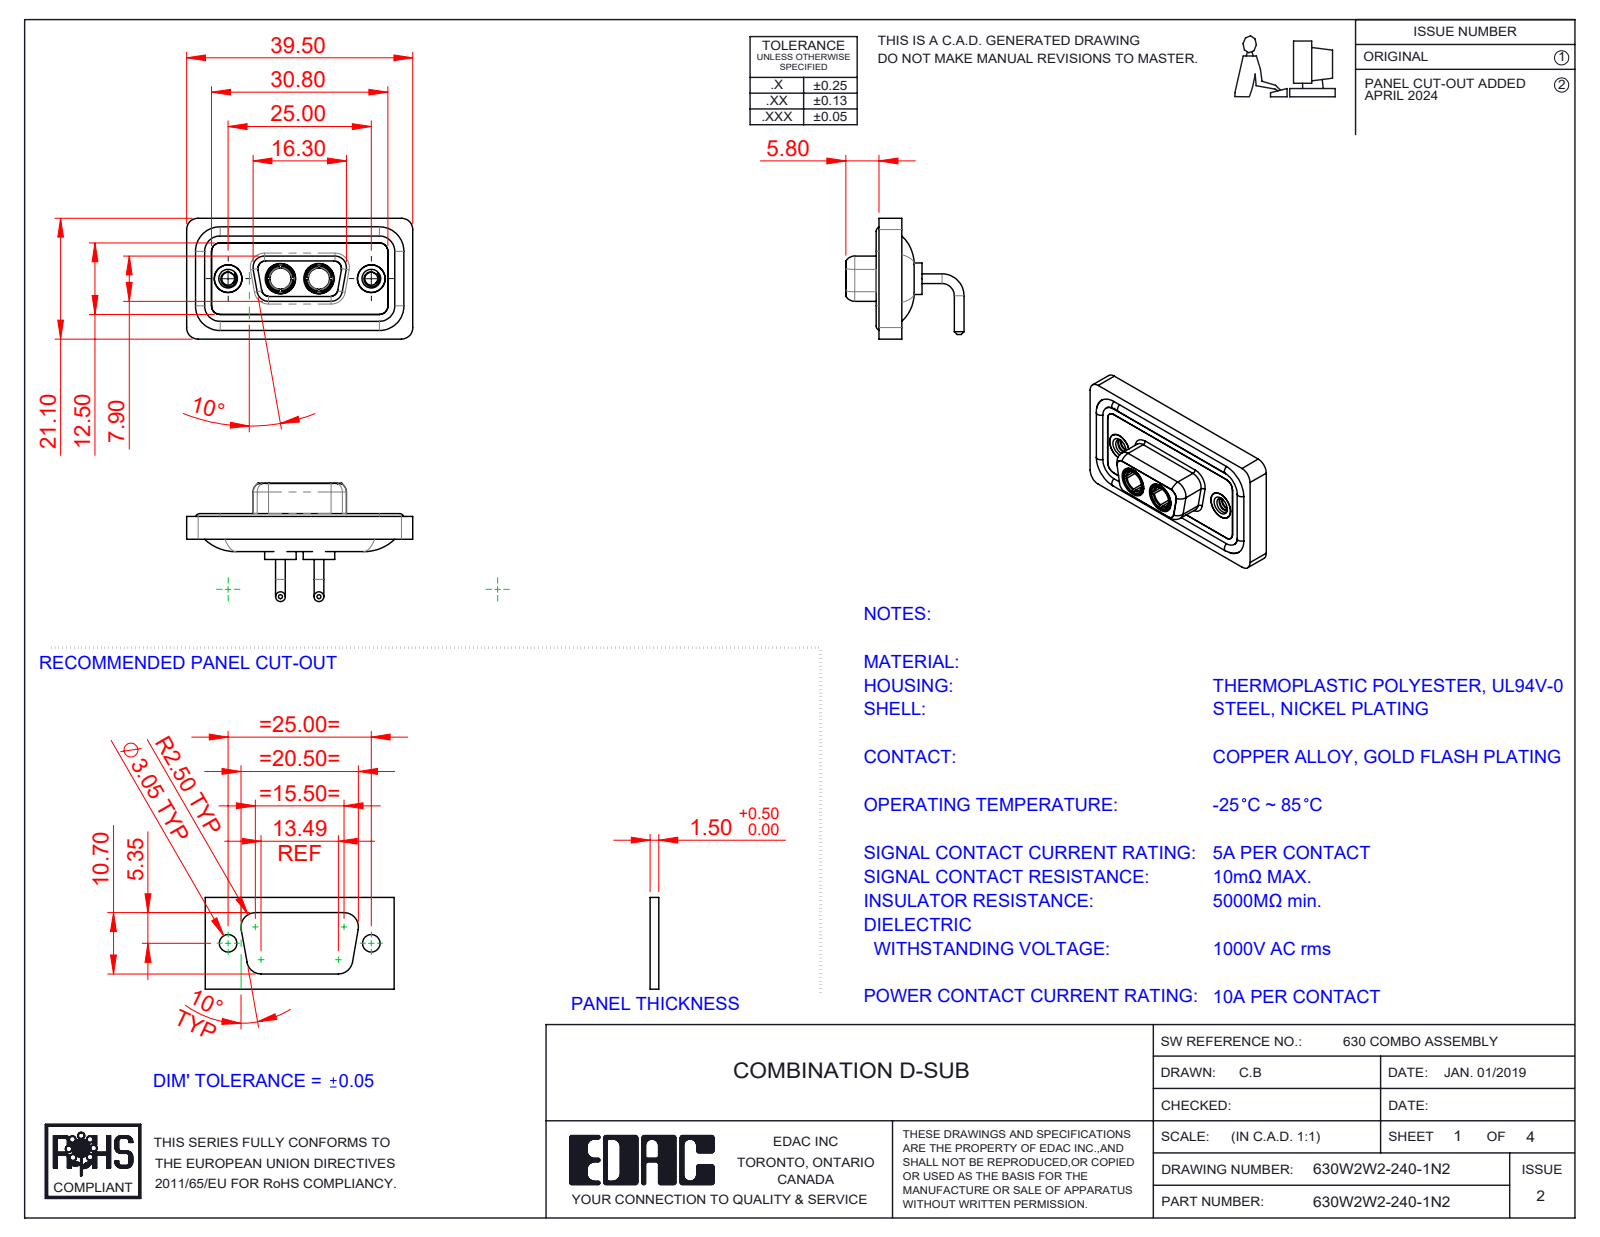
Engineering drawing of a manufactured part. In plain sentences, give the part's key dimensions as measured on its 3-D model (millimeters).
The part is named "630Combo Waterproof Housing_09 Contacts; Power Socket_10A RA; 630W2W2-240-1N2; 630Combo Housing_2W2 (+3 more)". Its 3-D file was written by "SolidWorks 2023 (CONFIG_CONTROL_DESIGN)". It is 11 solids with 542 faces: 163 planar, 238 cylindrical and 141 other. Overall it measures 39.5 by 21.1 by 20.65 millimeters. Its volume is 4 700 cubic millimeters and its surface area 7 684 square millimeters. Round holes: 4 of diameter 4.85, 2 of diameter 2.26, 2 of diameter 3.7, 2 of diameter 4, 2 of diameter 4.05, 2 of diameter 5, 2 of diameter 5.3. Round bosses or shafts: 4 of diameter 1.7, 4 of diameter 1.6, 2 of diameter 5.5, 2 of diameter 5.2, 2 of diameter 4.96, 2 of diameter 4.95, 2 of diameter 4.8, 2 of diameter 4.75. Partial cylindrical surfaces (rounded edges, fillets, slot ends): 18 of radius 1.5, 18 of radius 2, 8 of radius 1.35, 8 of radius 1.6, 4 of radius 0.25, 4 of radius 0.5, 4 of radius 0.6, 4 of radius 0.65. The main face-to-face distances are 0.4, 1.8, 1.1, 2.9, 2.5, 1.6, 3.1, 1.5, 2.1, 0.5. The hole center spacings are 9.14, 15.86, 6.72, 25.
